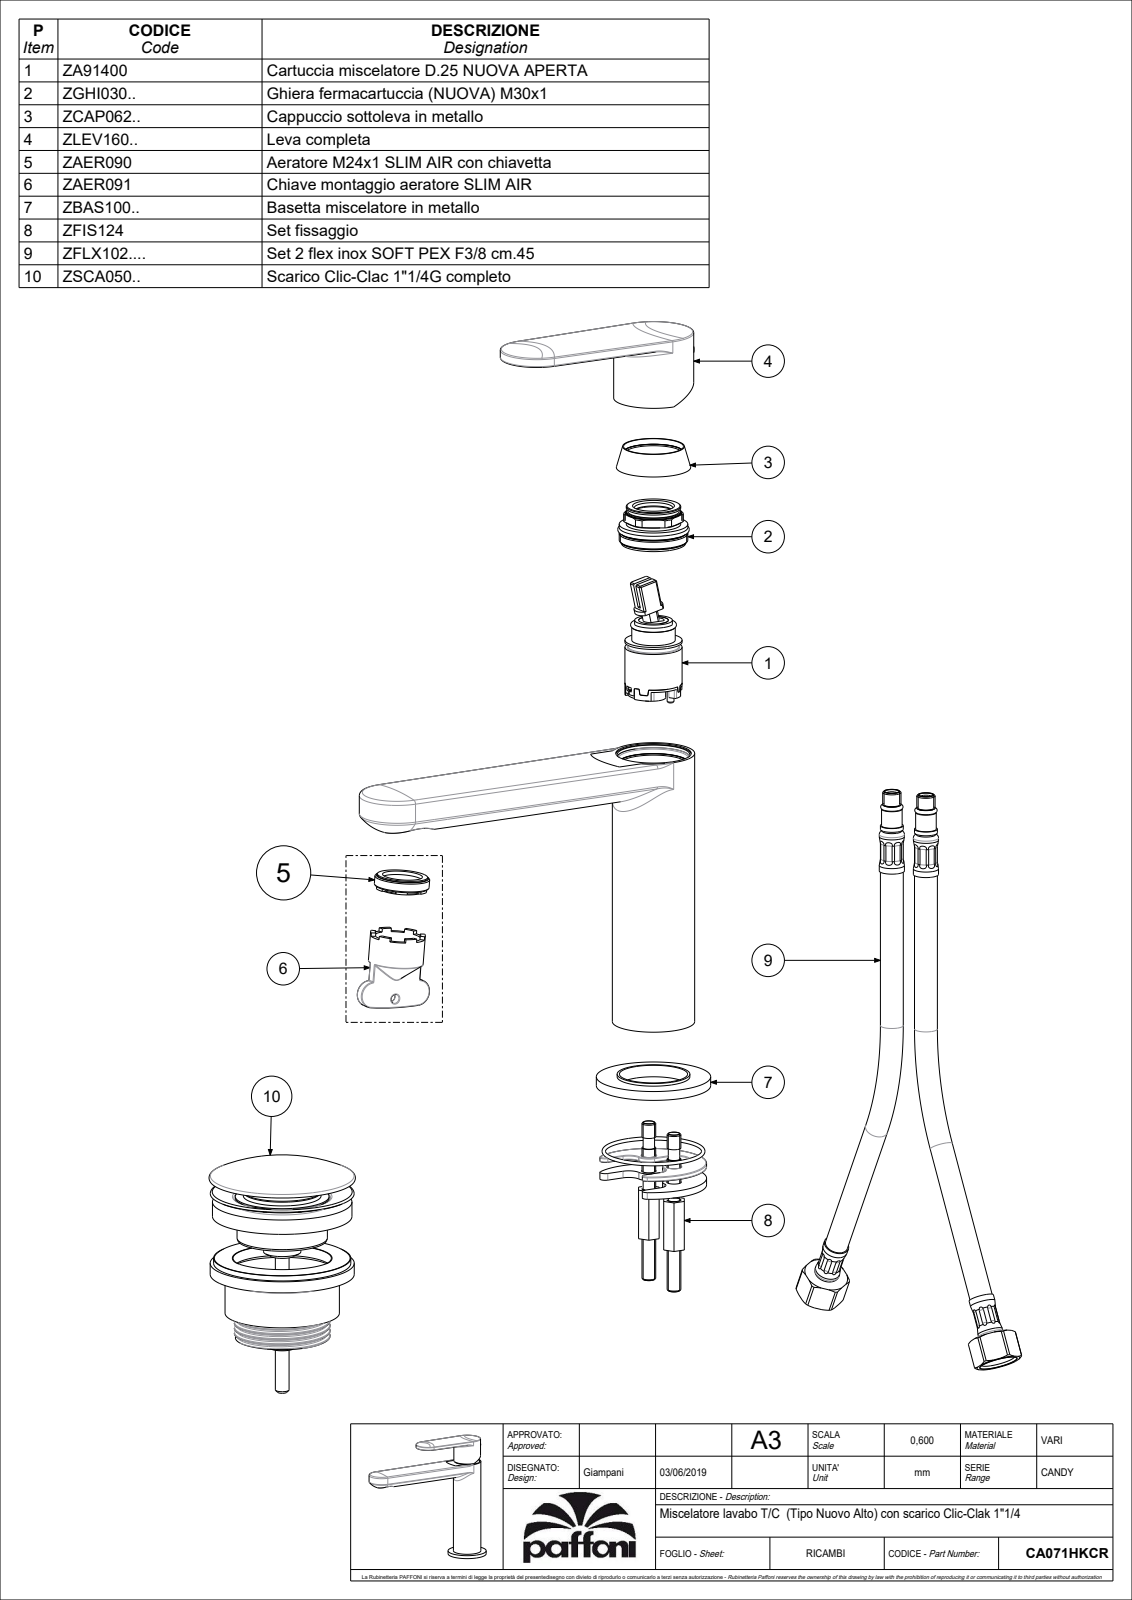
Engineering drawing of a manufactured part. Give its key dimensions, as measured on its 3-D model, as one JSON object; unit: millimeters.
{"part_name": "CA071HCR", "step_written_by": "CREO PARAMETRIC BY PTC INC, 2020044 (CONFIG_CONTROL_DESIGN)", "units": "millimeters", "bodies": {"solids": 2, "faces": 190, "planar": 61, "cylindrical": 57, "other": 72}, "overall_size": [171, 157.92, 50], "volume_mm3": 223417, "surface_area_mm2": 45306, "round_holes": [[3, 1], [4.5, 1], [24.5, 1], [24.8, 1], [26.2, 1], [28, 1]], "round_bosses_or_shafts": [[50, 1], [36, 1], [35, 1], [24, 1], [18.5, 1], [7.6, 1], [5.5, 1]], "partial_cylinders_radius": [[3, 4], [3.5, 1], [9.75, 1], [11.5, 1], [16, 1], [16.5, 1]], "face_to_face_distances": [4, 126, 122, 154.92, 150.92, 28.92, 2.5, 11.5, 9, 14]}
